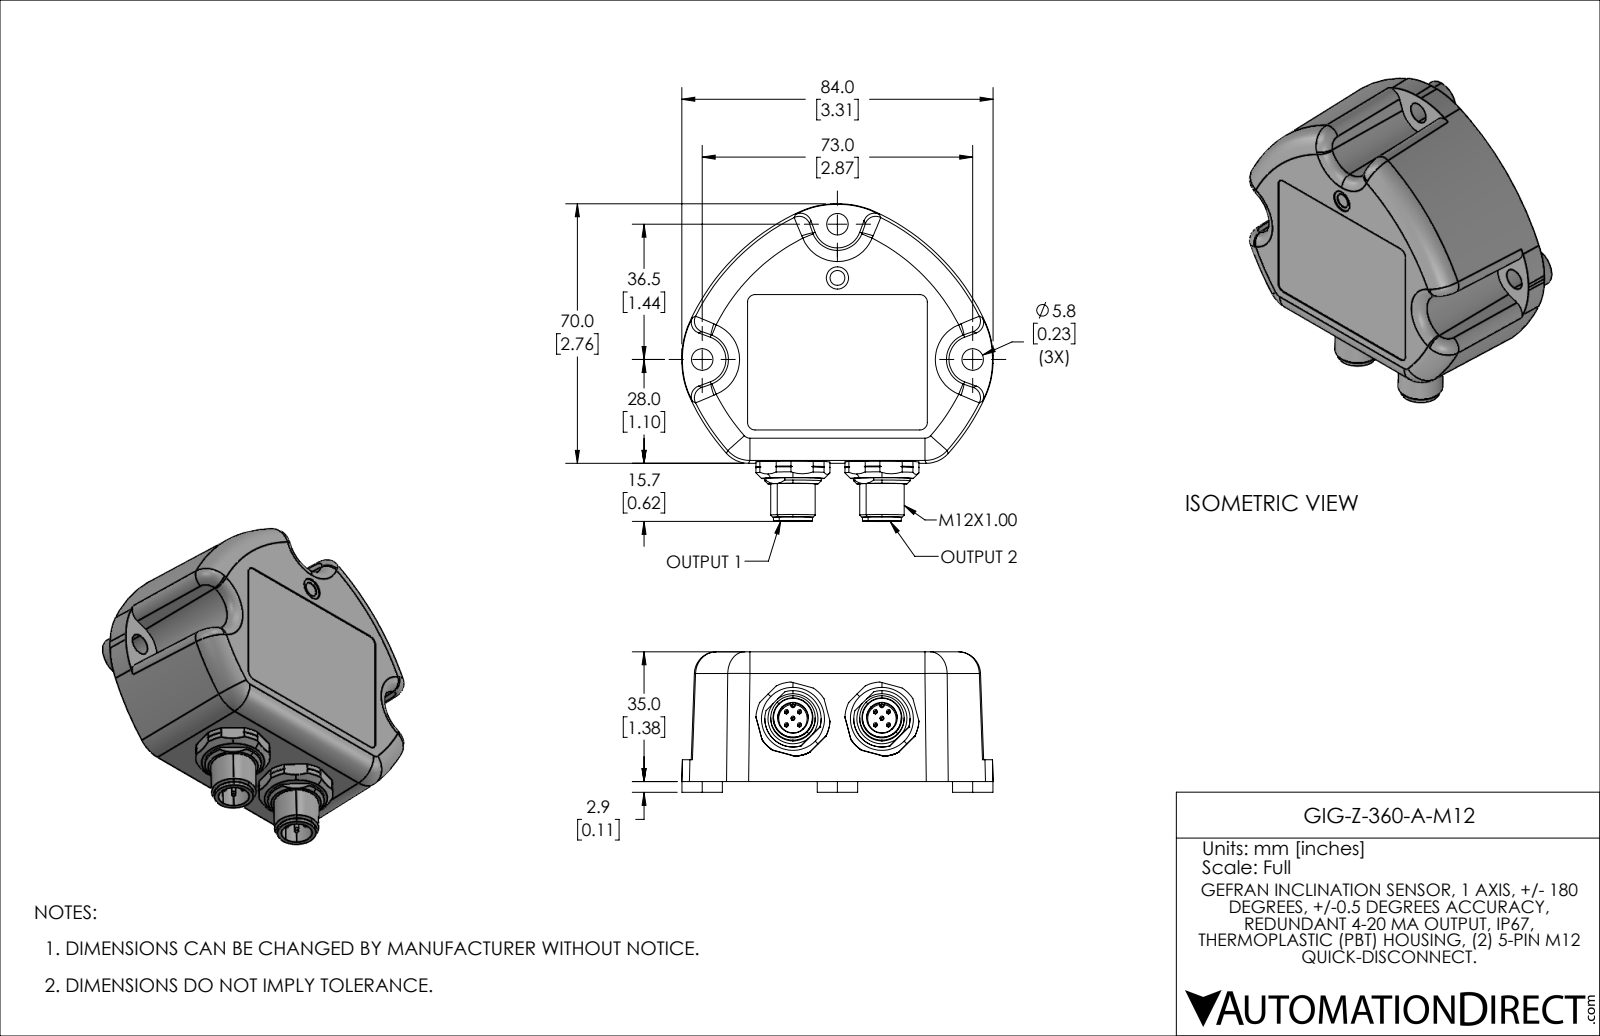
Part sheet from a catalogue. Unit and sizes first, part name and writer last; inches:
Units: inches
Overall size (bounding box): 3.374 × 3.307 × 1.492
Round holes (diameter × count): ⌀0.228 ×3, ⌀0.327 ×2, ⌀0.157 ×1, ⌀0.236 ×1
Round bosses / shafts (diameter × count): ⌀0.039 ×10, ⌀0.429 ×3, ⌀0.472 ×2, ⌀0.413 ×2
Partial cylindrical surfaces — rounded edges, fillets, slot ends (radius × count): R0.02 ×4, R0.079 ×4, R0.299 ×3, R0.024 ×2, R0.273 ×2, R0.394 ×2, R0.236 ×1, R0.301 ×1
Main face-to-face distances: 1.37, 1.378, 0.232, 1.138, 1.146, 0.114, 0.346, 1.484, 1.492, 0.668
Hole centre spacings: 1.678, 2.032, 0.571, 0.945, 2.874
Volume: 9.029 in³ · Surface area: 32.38 in²
Bodies: 1 solid, 365 faces (87 planar, 123 cylindrical, 155 other)
Part name (STEP PRODUCT): GIG-Z-360-A-M12
STEP written by: SolidWorks 2021 (AUTOMOTIVE_DESIGN)
